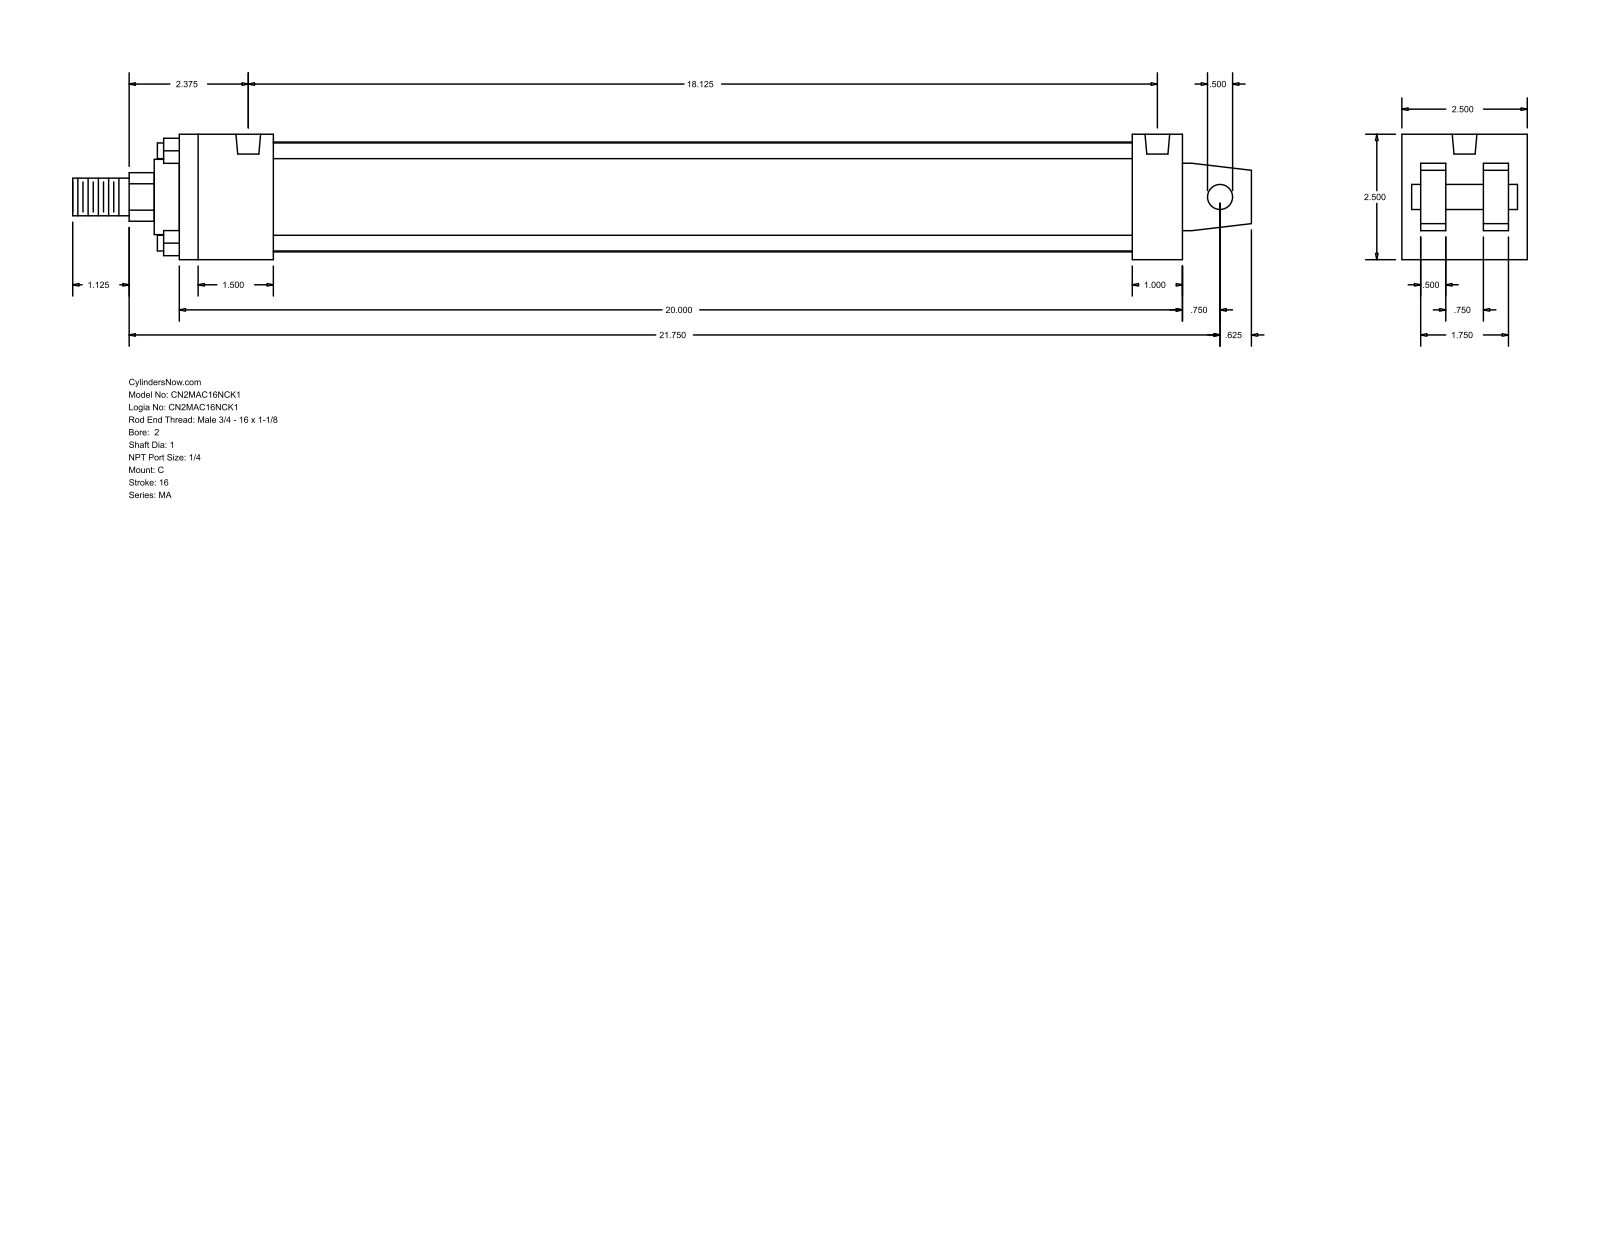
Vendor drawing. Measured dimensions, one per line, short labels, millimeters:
name: MA_C__0200_1
written by: GSSL Pune (CONFIG_CONTROL_DESIGN)
unit: mm
bodies: 0 solids, 103 faces (76 planar, 27 cylindrical, 0 other)
size: 596.9 × 63.5 × 63.5
holes: 4× ⌀7.94, 2× ⌀12.49
bosses: 4× ⌀7.94, 1× ⌀55.63, 1× ⌀38.1, 1× ⌀25.4, 1× ⌀19.05, 1× ⌀12.7
rounds: 1× R12.29
face distances: 63.5, 12.7, 508, 22.22, 41.28, 9.52, 53.98, 31.76, 47.63, 25.4
hole spacings: 460.37
